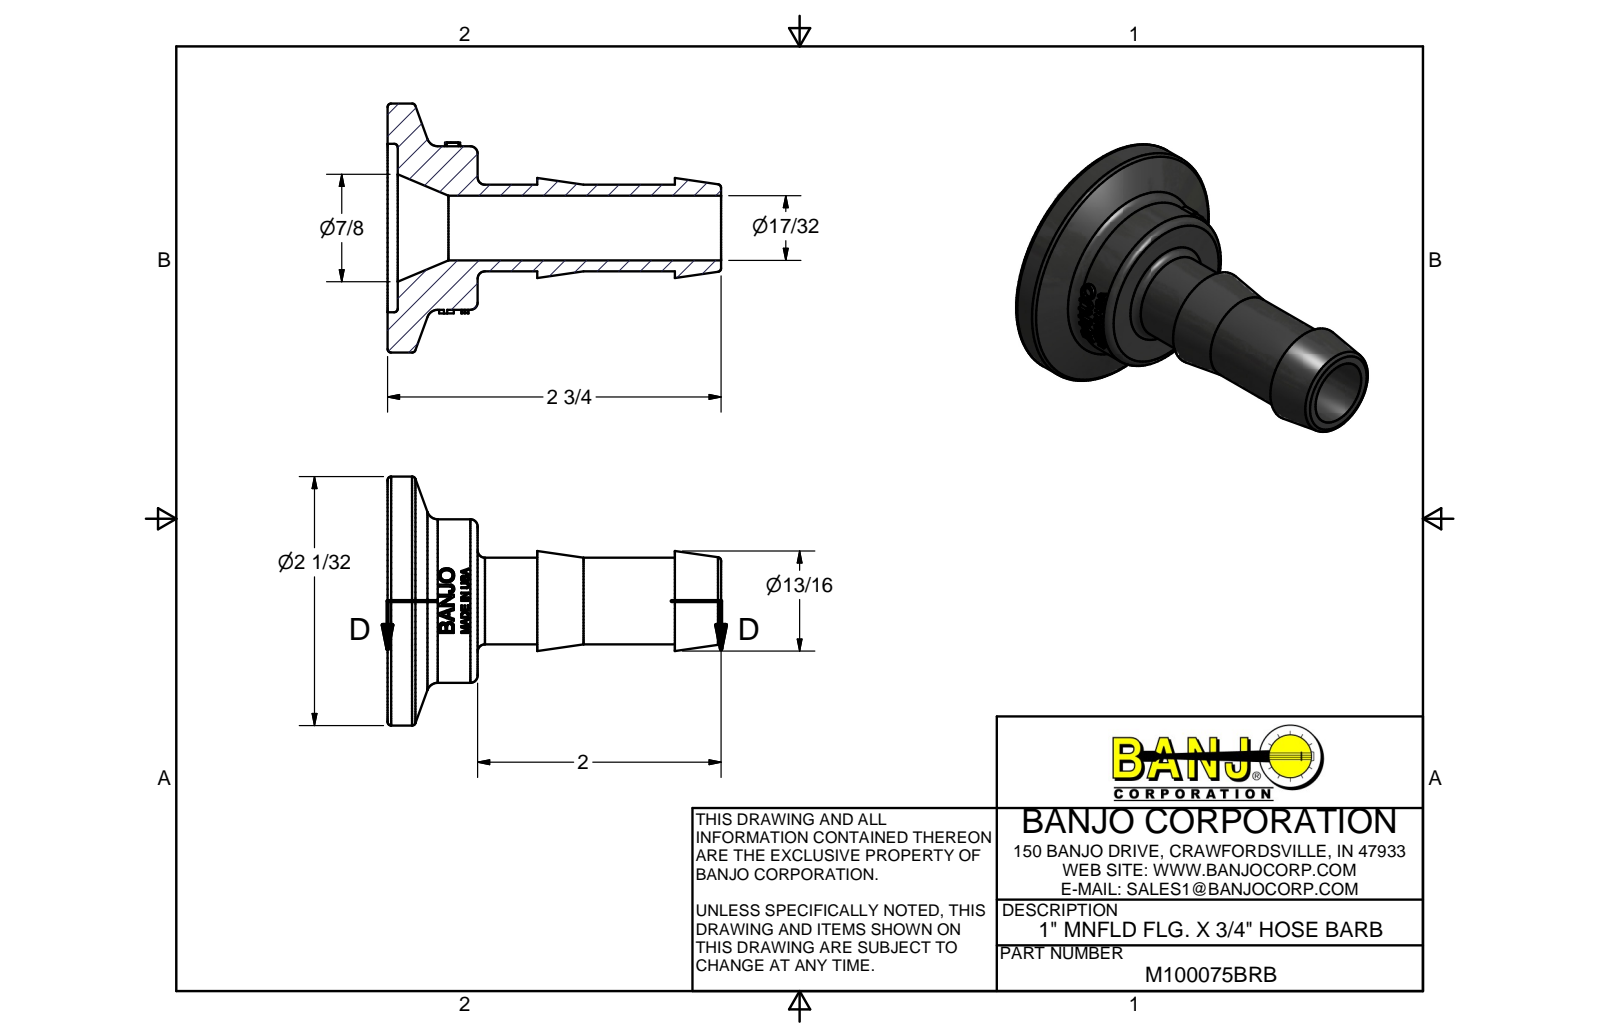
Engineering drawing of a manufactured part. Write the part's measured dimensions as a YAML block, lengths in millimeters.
part_name: "M100075BRB"
step_written_by: "Autodesk Inventor 2014 (AUTOMOTIVE_DESIGN)"
units: millimeters
bodies: {solids: 1, faces: 391, planar: 191, cylindrical: 46, other: 154}
overall_size: [69.6, 51.82, 51.82]
volume: 26624
surface_area: 12153
round_holes:
  - {diameter: 13.46, count: 1}
  - {diameter: 35.05, count: 1}
round_bosses_or_shafts:
  - {diameter: 51.82, count: 1}
  - {diameter: 34.04, count: 1}
  - {diameter: 18.03, count: 1}
partial_cylinders:
  - {radius: 17.78, count: 1}
face_to_face_distances: [2.14, 16.66, 18.8, 41.15, 57.81, 59.95, 28.7, 12.45, 29.11, 31.25]
